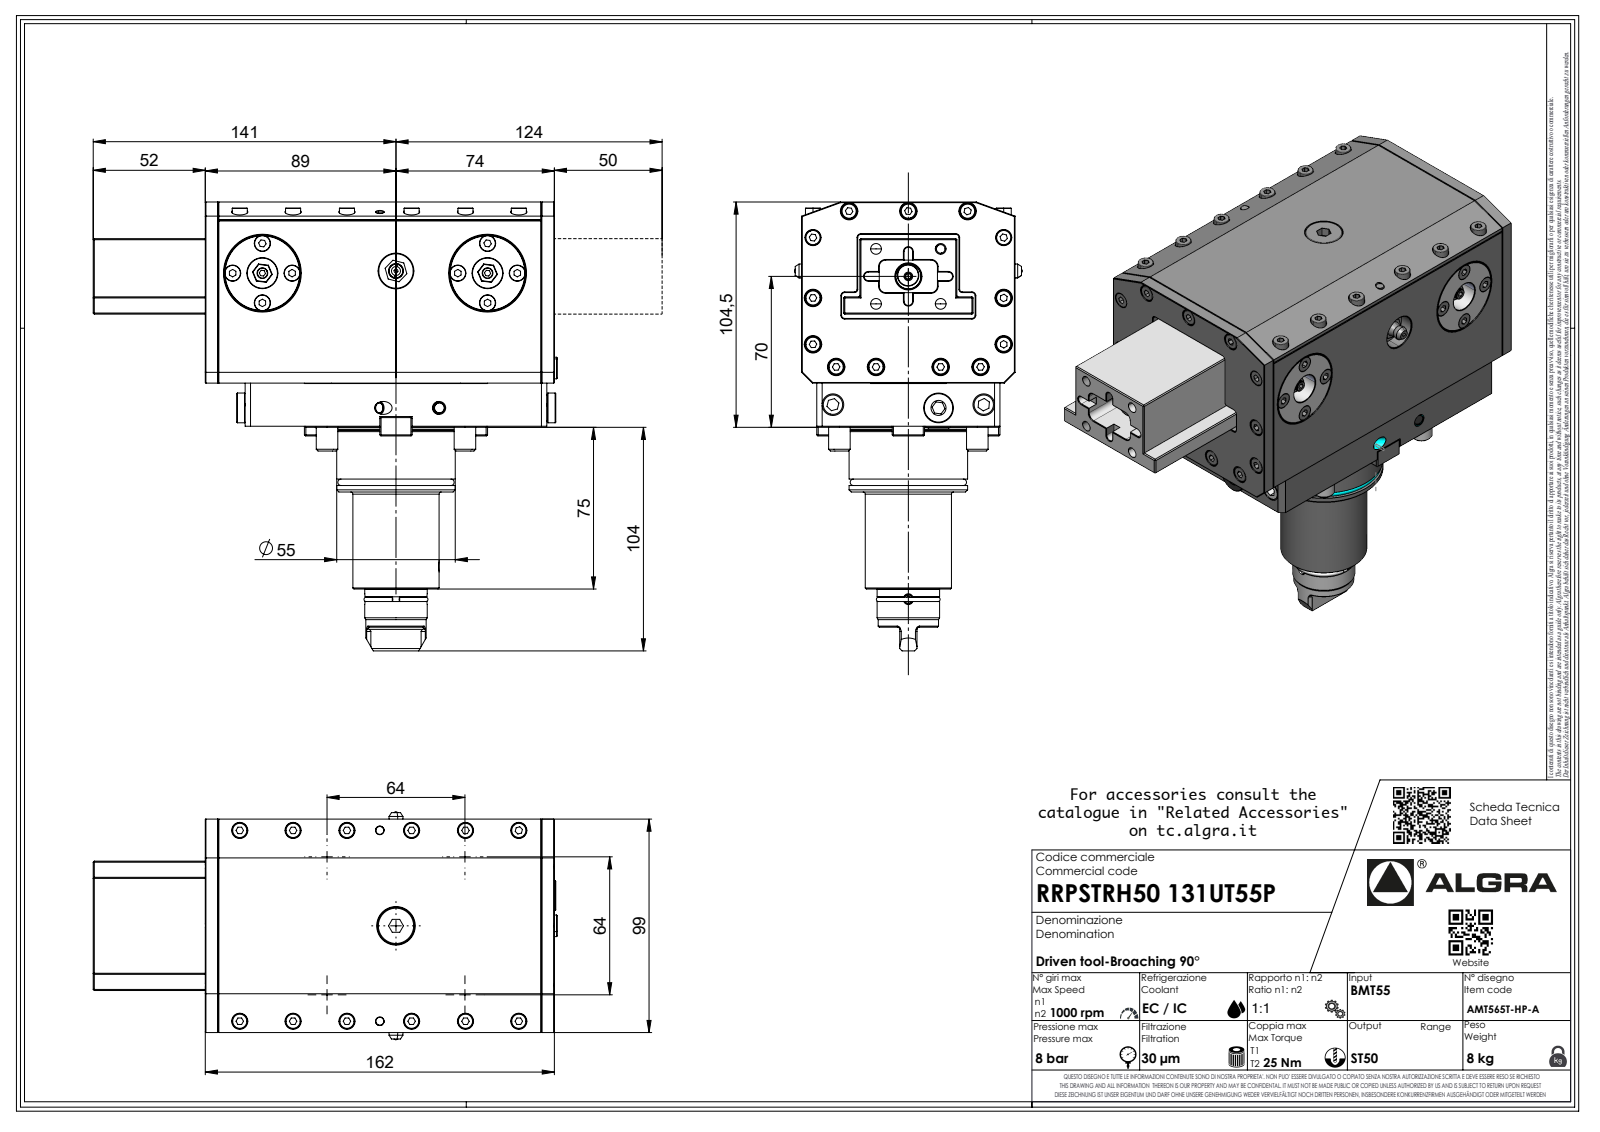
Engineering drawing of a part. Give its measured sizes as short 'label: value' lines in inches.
name: RRPSTRH50131UT55P
written by: SolidWorks 2023 (AUTOMOTIVE_DESIGN)
unit: in
bodies: 1 solid, 815 faces (532 planar, 118 cylindrical, 165 other)
size: 8.478 × 8.209 × 4.157
volume: 112 in³; area: 196.2 in²
holes: 1× ⌀0.083, 1× ⌀0.197, 1× ⌀2.402
bosses: 12× ⌀0.276, 1× ⌀2.165, 1× ⌀2.15, 1× ⌀1.976, 1× ⌀1.575, 1× ⌀1.142, 1× ⌀1.102, 1× ⌀0.394
rounds: 12× R0.098, 8× R0.394, 7× R0.013, 7× R0.02, 7× R0.146, 6× R0.079, 4× R0.118, 4× R0.315
face distances: 3.898, 3.307, 0.02, 0.787, 3.315, 2.047, 4.094, 0.78, 6.378, 3.917
hole spacings: 2.176
